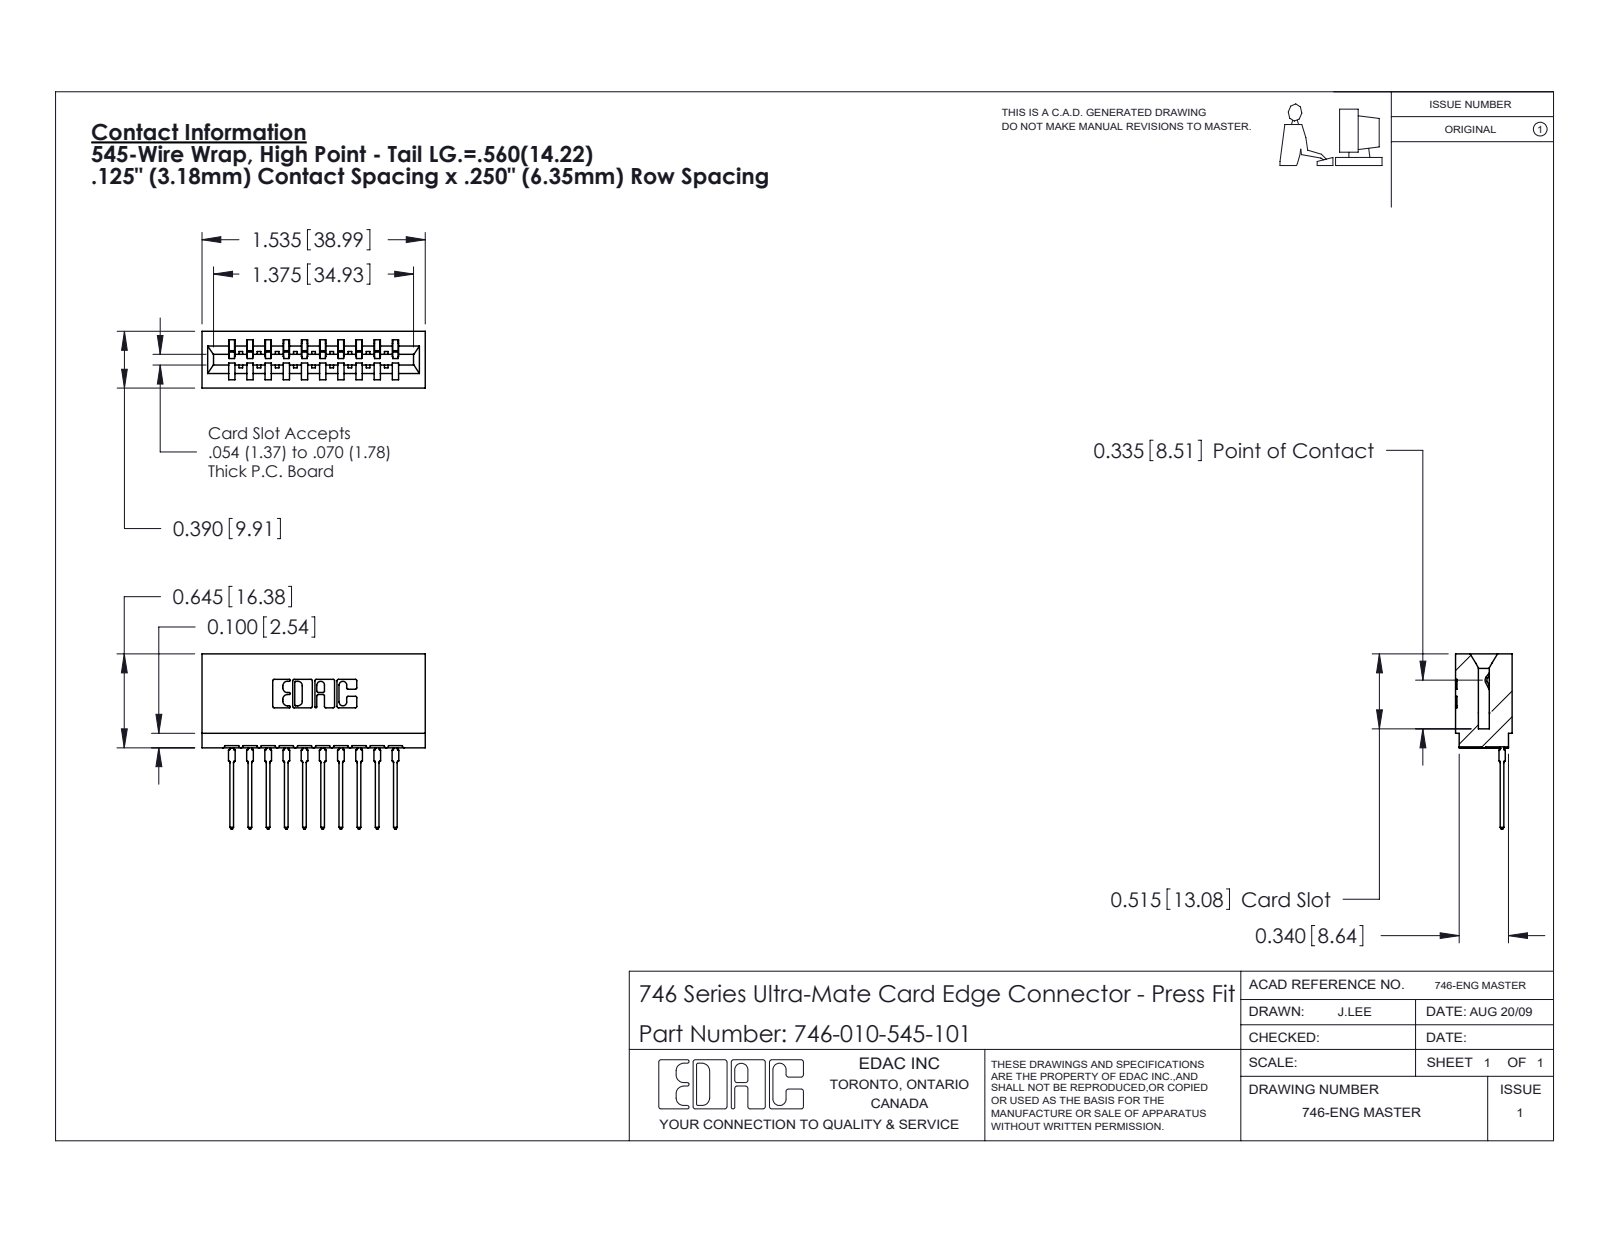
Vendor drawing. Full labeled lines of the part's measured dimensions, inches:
Part name (STEP PRODUCT): 746-010-545-101; 746-292-001_545; 746 Part_.515 Slot Depth - 01
STEP written by: SolidWorks 2020 (CONFIG_CONTROL_DESIGN)
Units: inches
Bodies: 11 solids, 1177 faces (685 planar, 232 cylindrical, 260 other)
Overall size (bounding box): 1.535 × 1.204 × 0.39
Volume: 0.264 in³ · Surface area: 9.309 in²
Partial cylindrical surfaces — rounded edges, fillets, slot ends (radius × count): R0.01 ×22, R0.021 ×20, R0.015 ×11, R0.007 ×6, R0.031 ×6, R0.005 ×4, R0.011 ×4, R0.026 ×3
Main face-to-face distances: 0.25, 0.5, 0.333, 0.057, 0.125, 0.042, 0.375, 0.208, 0.125, 0.39
